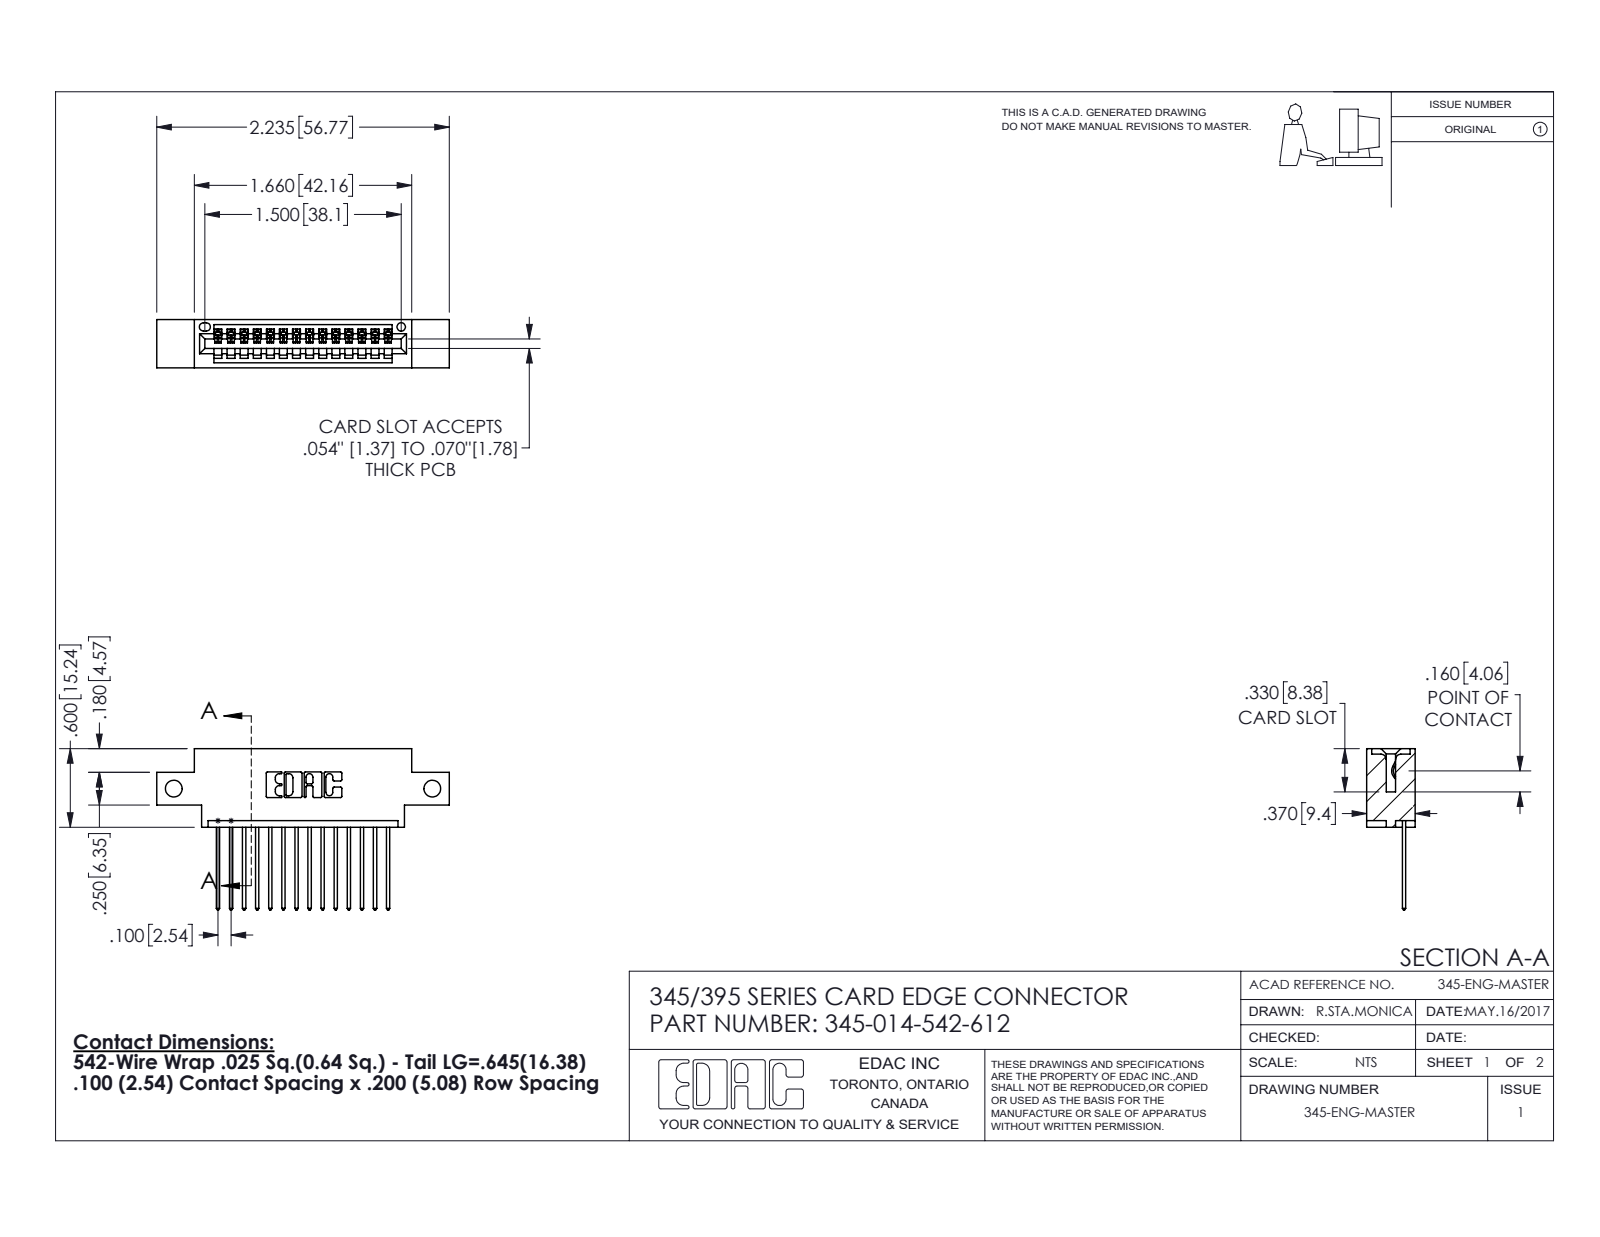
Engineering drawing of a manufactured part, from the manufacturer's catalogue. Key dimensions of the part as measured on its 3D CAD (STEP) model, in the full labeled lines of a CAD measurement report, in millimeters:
Part name (STEP PRODUCT): 345-014-542-612; 345-292-001_345-293-142; 345 Part_0.170 Offset - Side Mount
STEP written by: SolidWorks 2016 (CONFIG_CONTROL_DESIGN)
Units: millimetres
Bodies: 15 solids, 942 faces (644 planar, 298 cylindrical, 0 other)
Overall size (bounding box): 56.8 × 31.3 × 9.4
Volume: 5 000 mm³ · Surface area: 6 436 mm²
Round holes (diameter × count): ⌀3.3 ×2, ⌀1.6 ×1
Partial cylindrical surfaces — rounded edges, fillets, slot ends (radius × count): R0.2 ×28, R0.3 ×28, R0.3 ×22, R0.2 ×6, R0.8 ×6, R0.7 ×3, R0.8 ×2, R1 ×2
Main face-to-face distances: 7.6, 1.8, 9.4, 5.1, 2.5, 6.9, 0.6, 2.5, 5.7, 3.8
Hole centre spacings: 50.2
